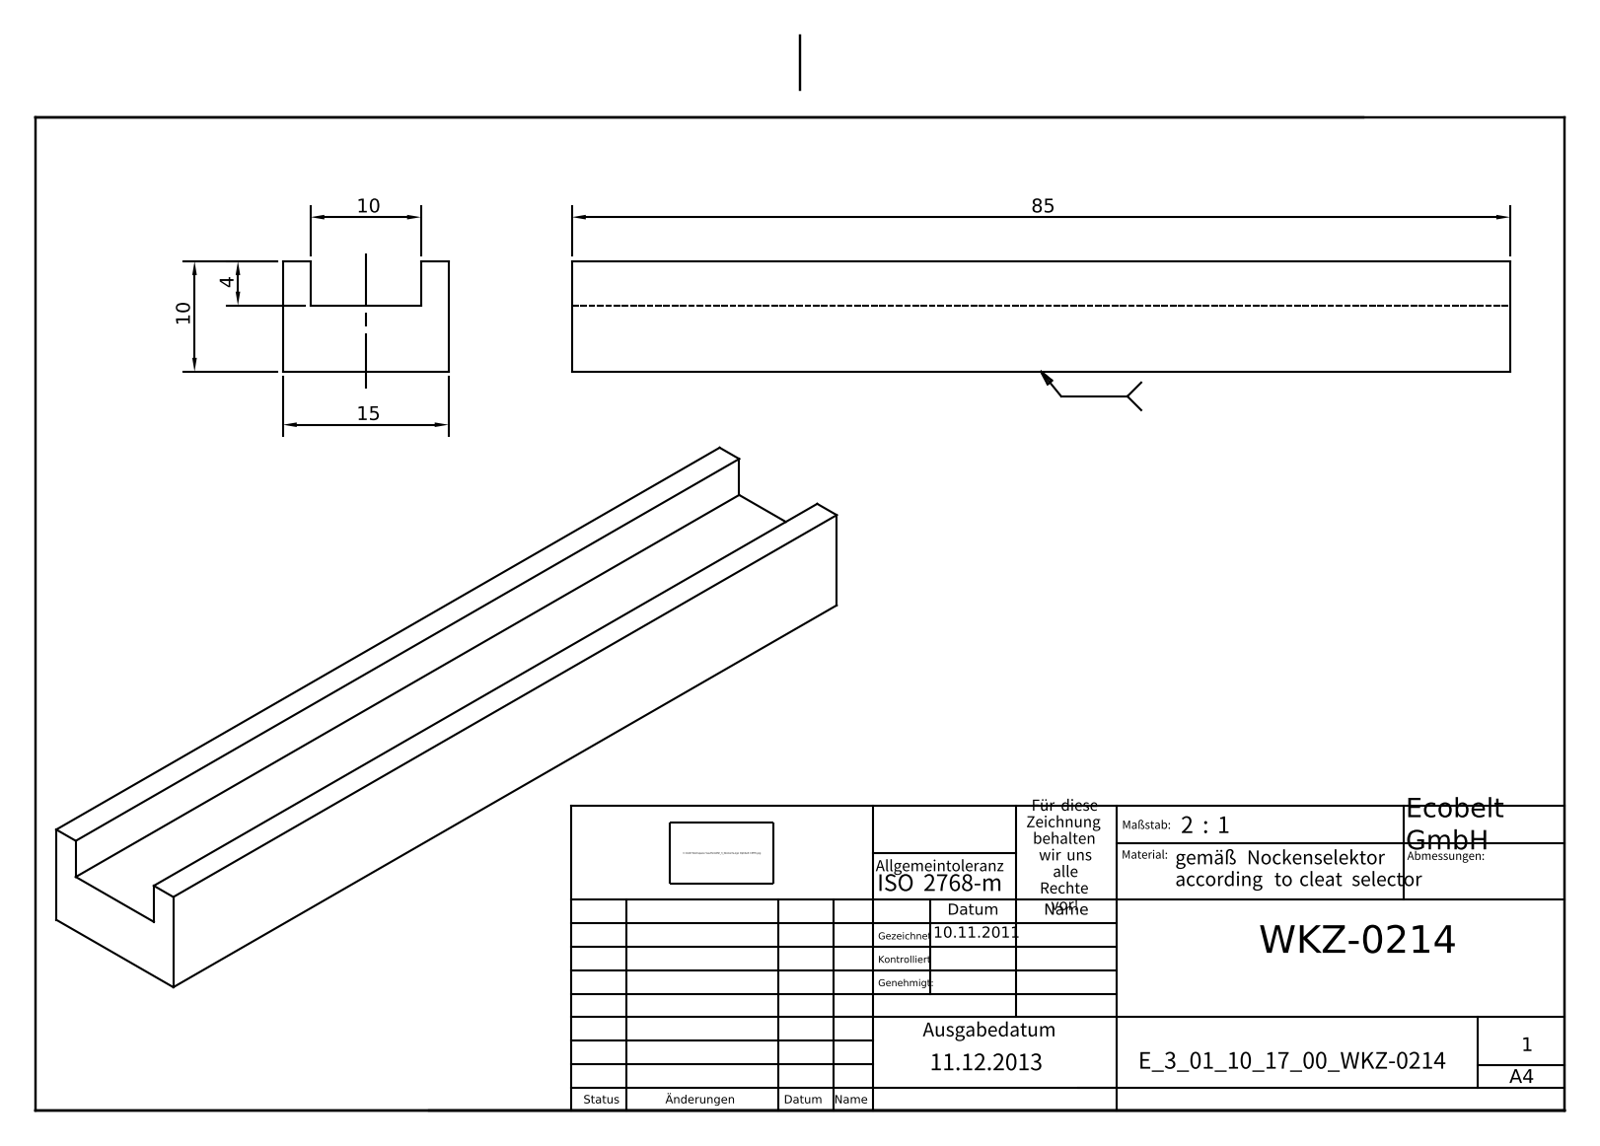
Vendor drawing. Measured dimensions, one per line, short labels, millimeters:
name: E_3_01_10_17_00_WKZ-0214
written by: Autodesk Inventor 2025 (AUTOMOTIVE_DESIGN)
unit: mm
bodies: 1 solid, 10 faces (10 planar, 0 cylindrical, 0 other)
size: 85 × 15 × 10
volume: 9 350 mm³; area: 5 150 mm²
face distances: 15, 6, 10, 2.5, 12.5, 4, 85
